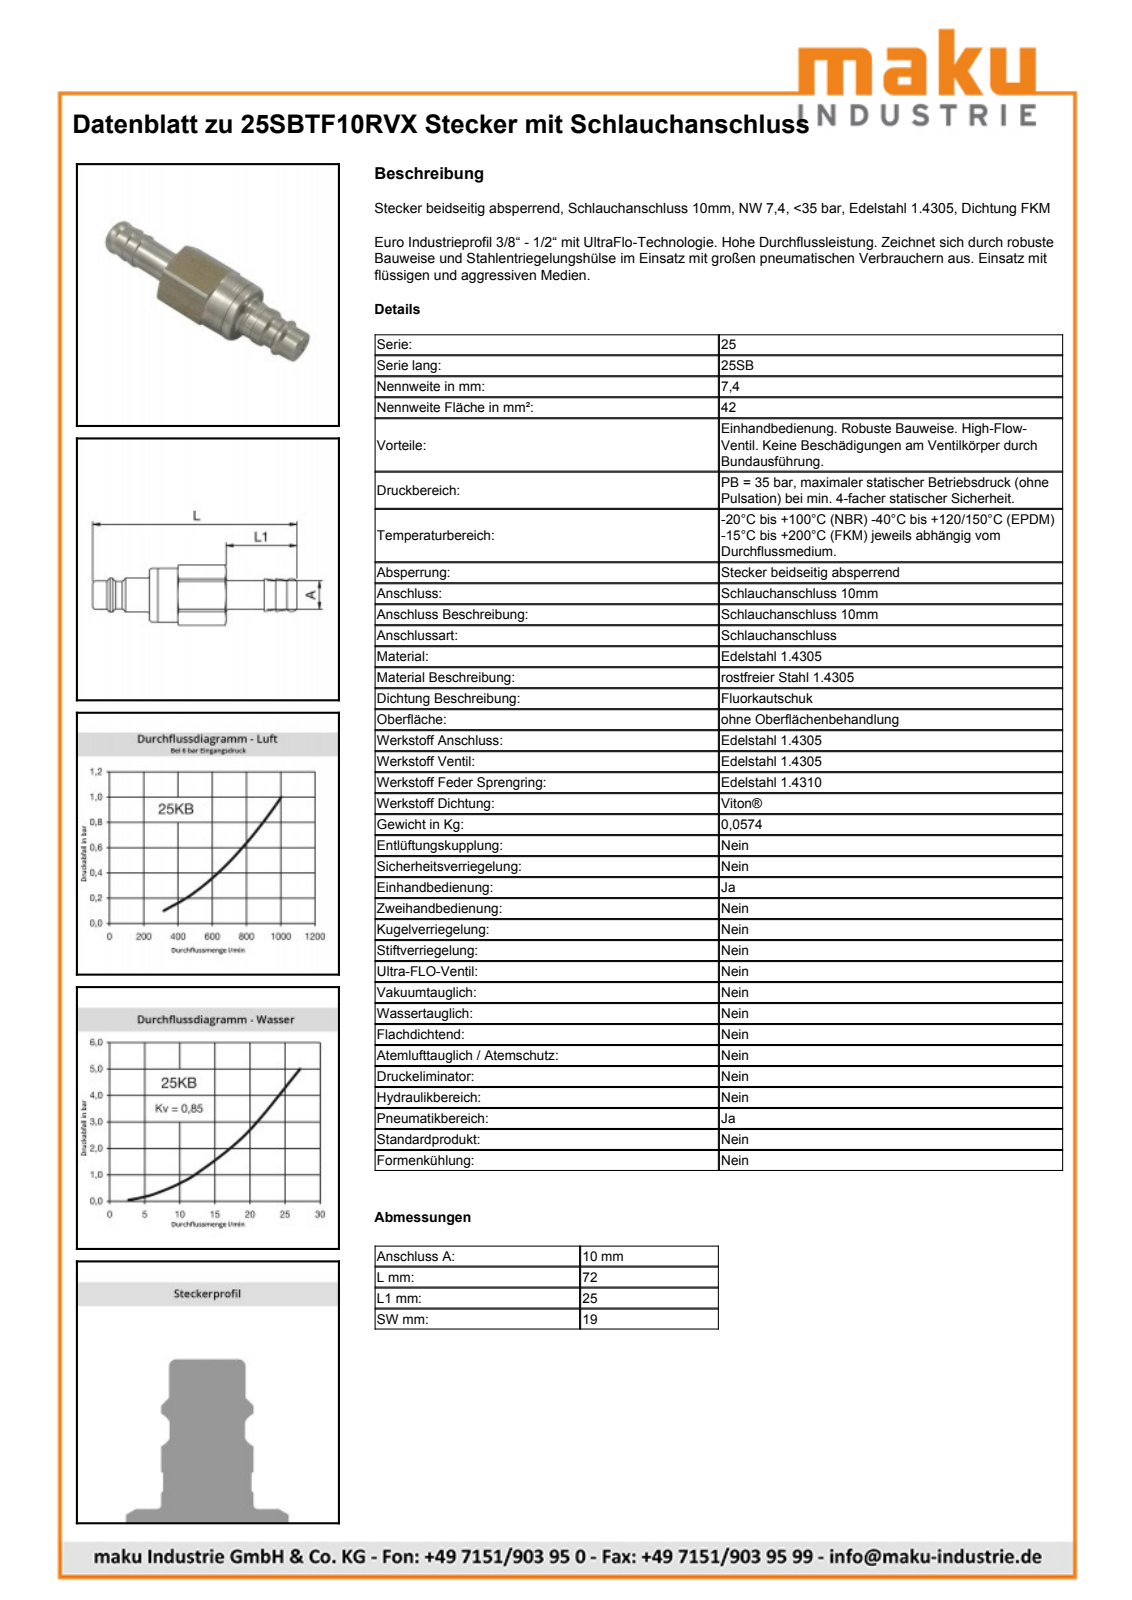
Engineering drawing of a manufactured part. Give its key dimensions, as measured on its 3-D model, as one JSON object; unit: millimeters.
{"part_name": "D105163", "step_written_by": "Autodesk Inventor 2013 (AUTOMOTIVE_DESIGN)", "units": "millimeters", "bodies": {"solids": 1, "faces": 55, "planar": 15, "cylindrical": 17, "other": 23}, "overall_size": [72, 21.38, 19.83], "volume_mm3": 12113, "surface_area_mm2": 4303, "round_holes": [[16, 1]], "round_bosses_or_shafts": [[19, 1], [18.95, 1], [15.27, 1], [12, 1], [10.1, 1], [9.9, 1], [9.75, 1]], "partial_cylinders_radius": [[10.7, 1]], "face_to_face_distances": [19, 27, 52, 25, 20, 47, 72, 3, 4.5, 27.5]}
